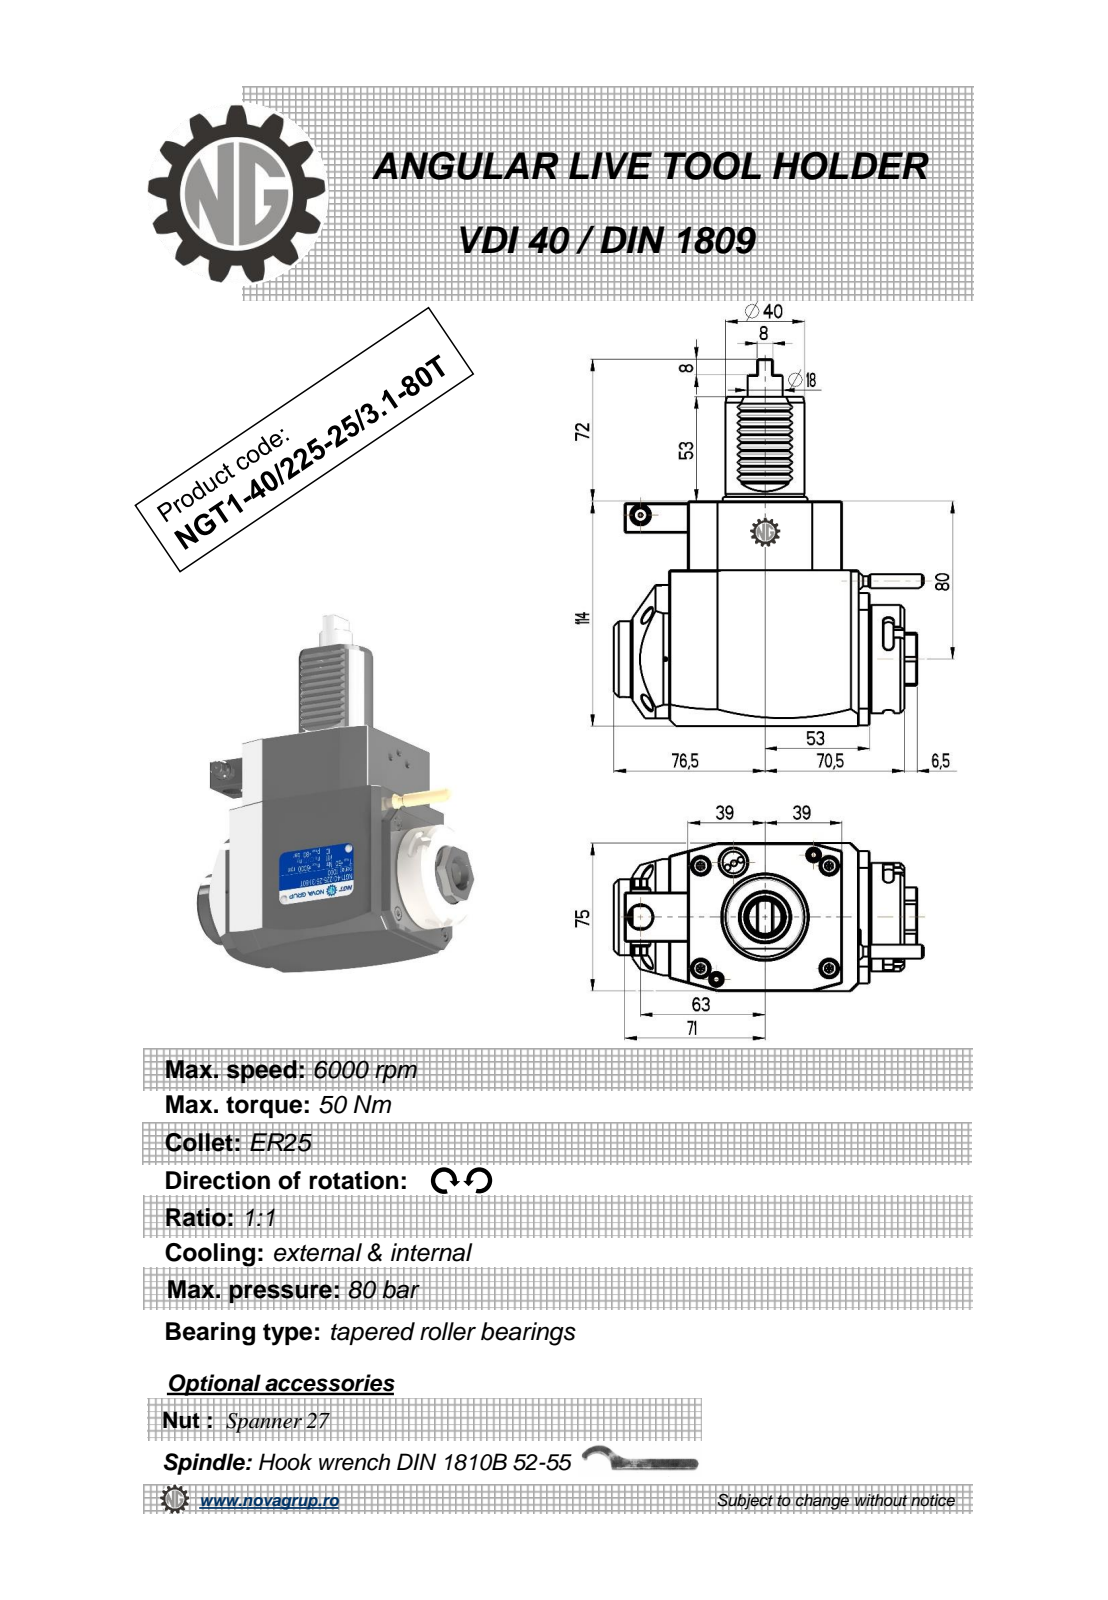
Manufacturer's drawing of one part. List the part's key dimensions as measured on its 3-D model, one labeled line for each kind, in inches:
Part name (STEP PRODUCT): NGT1_40_225_25_3_1_80T
STEP written by: PRO/ENGINEER BY PARAMETRIC TECHNOLOGY CORPORATION, 2010280 (CONFIG_CONTROL_DESIGN)
Units: inches
Bodies: 1 solid, 355 faces (187 planar, 92 cylindrical, 76 other)
Overall size (bounding box): 7.323 × 6.174 × 2.953
Volume: 58.58 in³ · Surface area: 110.7 in²
Round holes (diameter × count): ⌀0.079 ×1, ⌀0.098 ×1, ⌀0.118 ×1, ⌀0.177 ×1, ⌀0.374 ×1, ⌀0.472 ×1, ⌀0.709 ×1
Round bosses / shafts (diameter × count): ⌀0.315 ×2, ⌀2.165 ×1, ⌀1.89 ×1, ⌀1.575 ×1, ⌀1.516 ×1, ⌀0.701 ×1, ⌀0.394 ×1, ⌀0.276 ×1
Partial cylindrical surfaces — rounded edges, fillets, slot ends (radius × count): R0.012 ×10, R0.098 ×6, R0.031 ×2, R7.087 ×2, R0.02 ×1, R0.152 ×1, R0.167 ×1, R0.591 ×1
Main face-to-face distances: 2.953, 4.488, 0.551, 0.689, 3.071, 3.622, 1.24, 4.311, 1.378, 0.157
Hole centre spacings: 1.47, 1.701, 2.854
